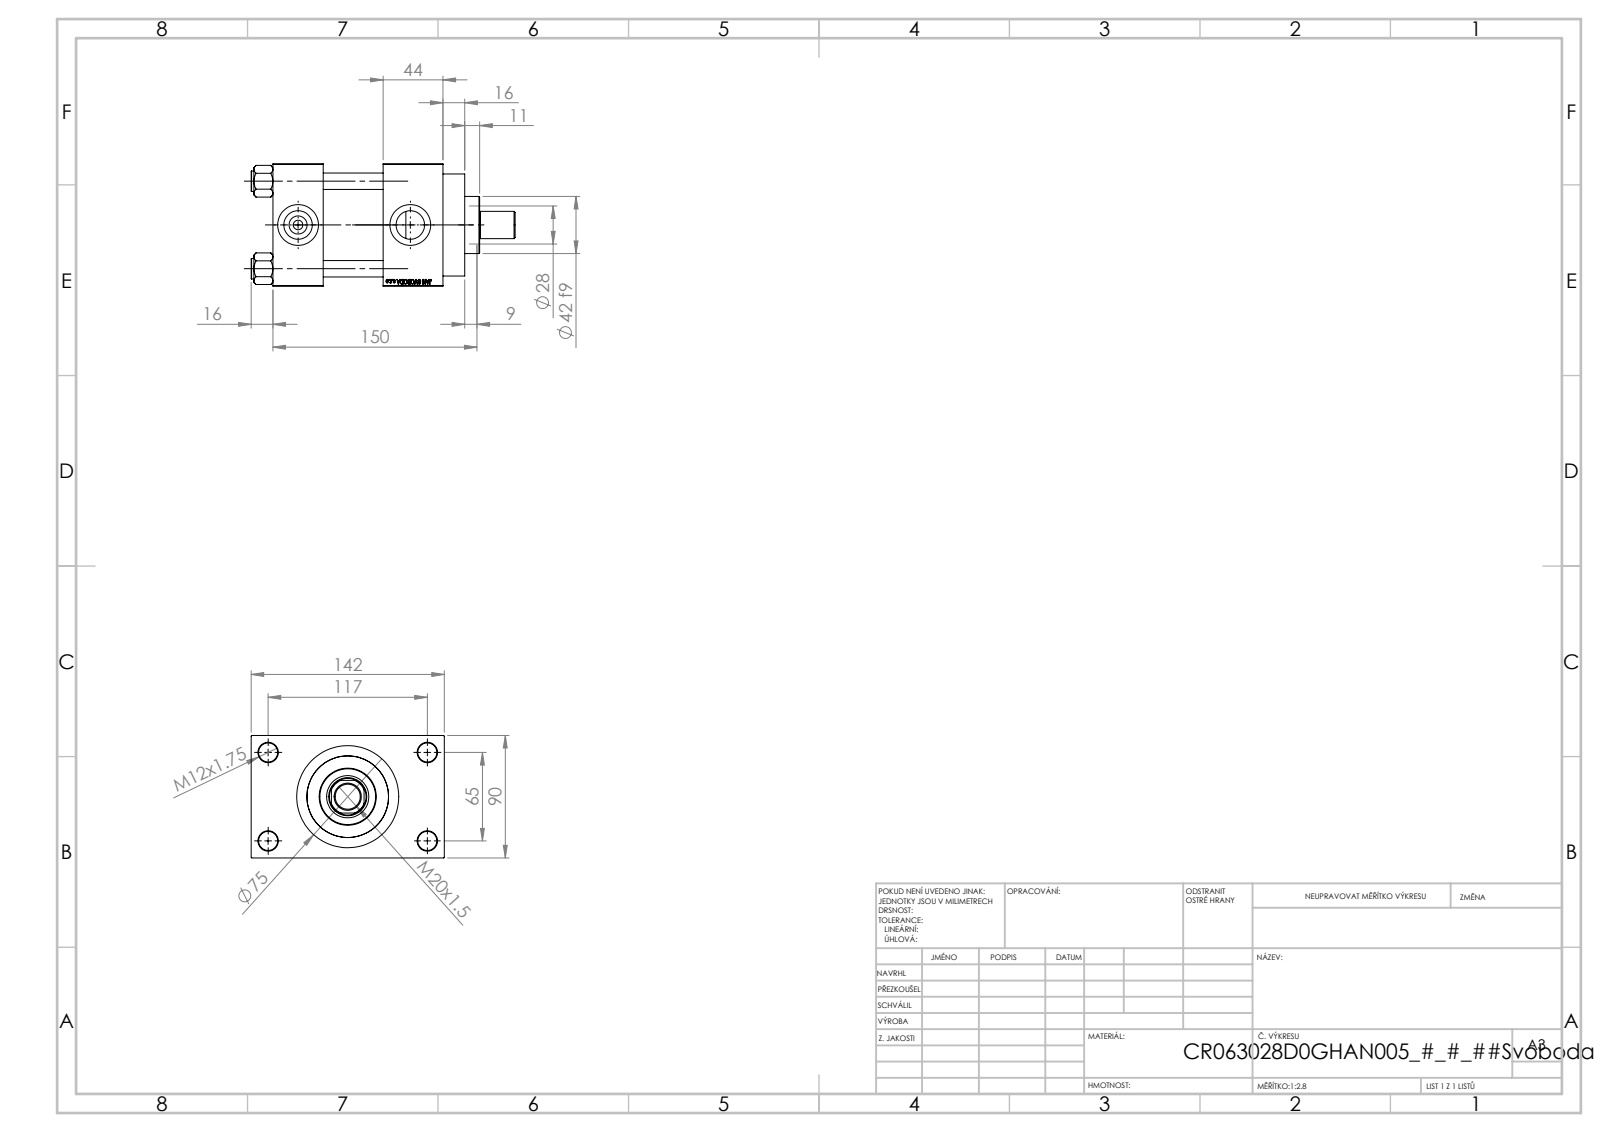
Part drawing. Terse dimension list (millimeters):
name: V215CR_D_Body; V215CR_D_TYCINKA; ROD_END_AH; NUT_M5_D (+2 more)
written by: SolidWorks 2019 (CONFIG_CONTROL_DESIGN)
unit: mm
bodies: 12 solids, 1117 faces (501 planar, 92 cylindrical, 524 other)
size: 194 × 142 × 90
volume: 1 036 000 mm³; area: 189 691 mm²
holes: 4× ⌀12, 4× ⌀14, 2× ⌀7, 2× ⌀20.96, 2× ⌀30, 1× ⌀18.5, 1× ⌀28, 1× ⌀31, 1× ⌀50, 1× ⌀60, 1× ⌀63
bosses: 4× ⌀15, 1× ⌀75, 1× ⌀69, 1× ⌀42, 1× ⌀20, 1× ⌀18
rounds: 1× R13.5
face distances: 44, 90, 37, 81, 88, 125, 26, 116, 141, 16
hole spacings: 26.35, 45.47, 64.3, 66.92, 69.81, 90.65, 111.34, 65
